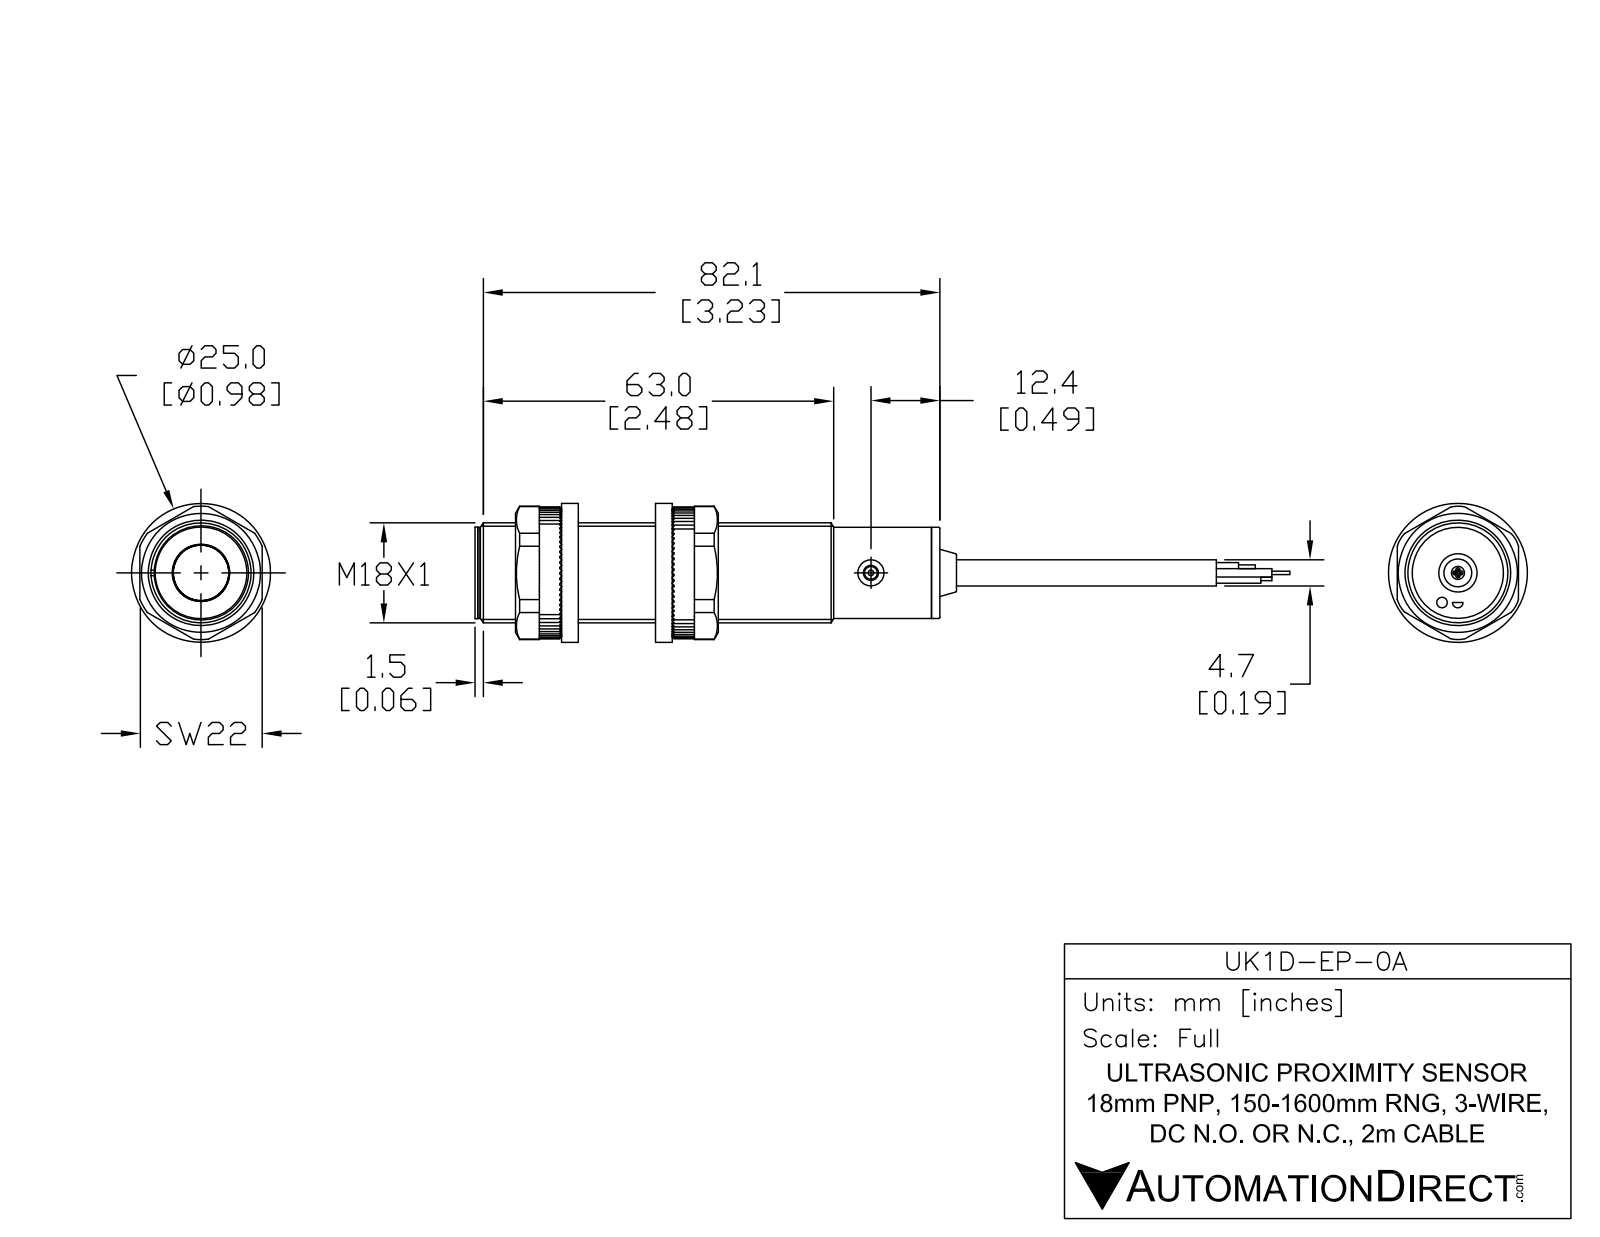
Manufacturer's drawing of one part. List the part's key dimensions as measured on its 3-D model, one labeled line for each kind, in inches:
Part name (STEP PRODUCT): UK1D-EP-0A
STEP written by: SolidWorks 2017 (AUTOMOTIVE_DESIGN)
Units: inches
Bodies: 6 solids, 55 faces (17 planar, 24 cylindrical, 14 other)
Overall size (bounding box): 4.832 × 0.709 × 0.709
Volume: 1.285 in³ · Surface area: 10.69 in²
Round holes (diameter × count): ⌀0.185 ×2, ⌀0.106 ×1
Round bosses / shafts (diameter × count): ⌀0.709 ×1, ⌀0.646 ×1, ⌀0.622 ×1, ⌀0.374 ×1, ⌀0.189 ×1, ⌀0.091 ×1
Main face-to-face distances: 3.193, 3.252, 0.059, 0.039, 3.232, 3.291, 0.041, 3.234, 3.293, 3.257
